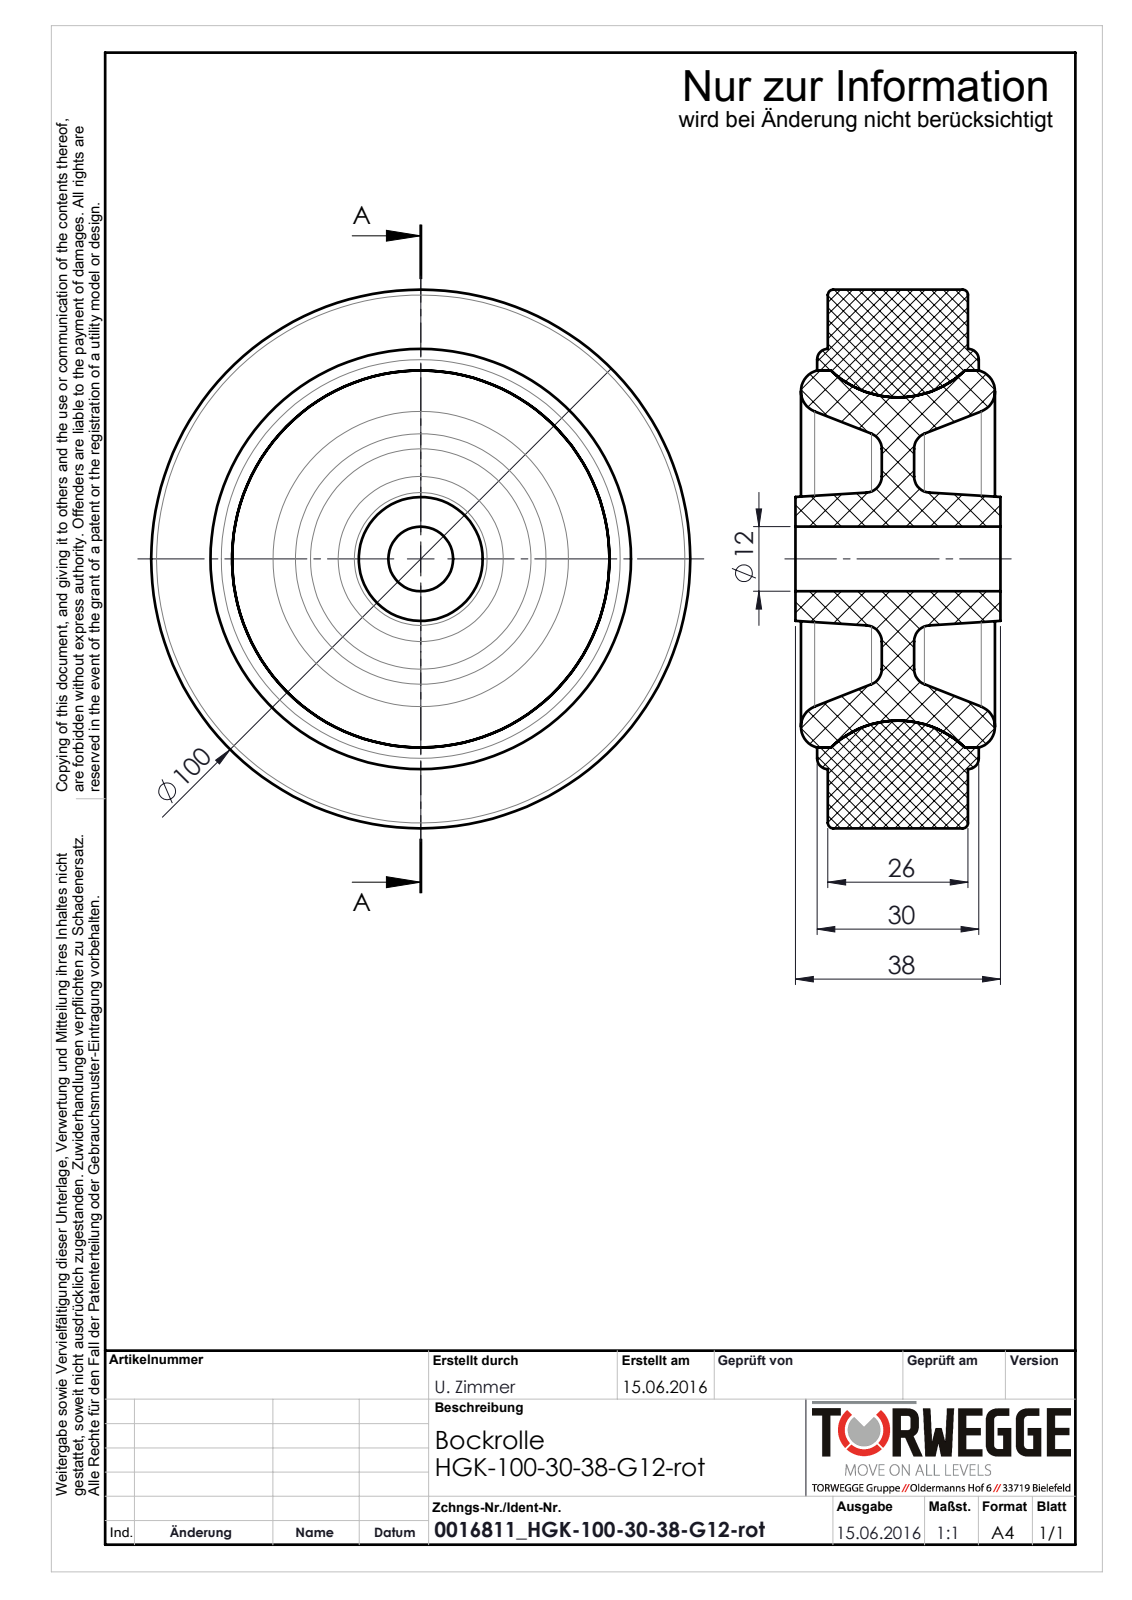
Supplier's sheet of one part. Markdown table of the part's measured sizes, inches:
| quantity | value |
| --- | --- |
| part name | 0016811_HGK-100-30-38-G12-rot |
| STEP written by | SolidWorks 2016 (AUTOMOTIVE_DESIGN) |
| units | inches |
| bodies | 2 solids, 56 faces (8 planar, 12 cylindrical, 36 other) |
| overall size | 3.937 × 3.937 × 1.496 |
| volume | 11.8 in³ |
| surface area | 68.45 in² |
| round holes (diameter × count) | 0.472 × 1, 2.756 × 1 |
| round bosses / shafts (diameter × count) | 3.937 × 1 |
| main face-to-face distances | 1.024, 0.63, 0.236, 0.394, 0.079, 0.472, 0.709, 1.102, 0.157, 0.866 |
